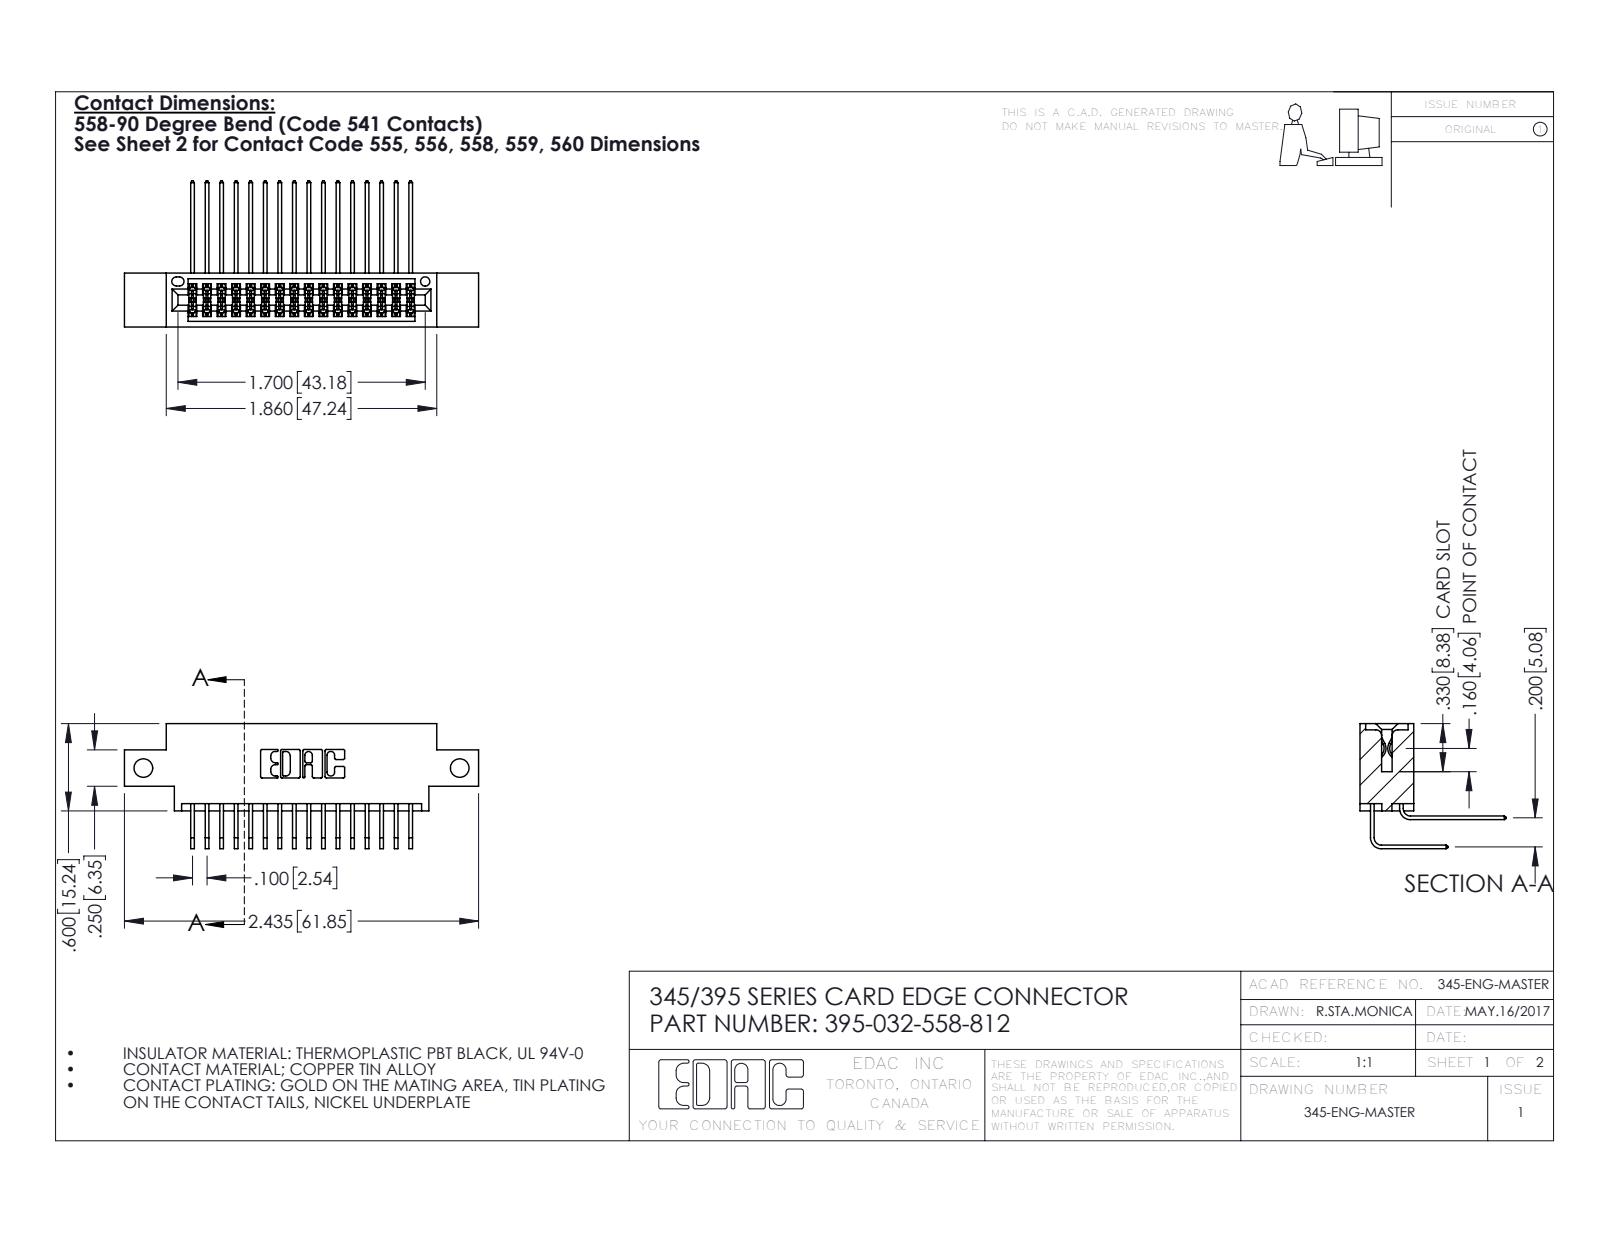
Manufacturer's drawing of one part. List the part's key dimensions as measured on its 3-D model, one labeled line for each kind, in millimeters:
Part name (STEP PRODUCT): 345-292-001_558 Tail - 2; 345 Part_0.170 Offset - Side Mount; 395-032-558-812; 345-292-001_558 559 Tail - 1
STEP written by: SolidWorks 2016 (CONFIG_CONTROL_DESIGN)
Units: millimetres
Bodies: 33 solids, 1794 faces (1204 planar, 590 cylindrical, 0 other)
Overall size (bounding box): 61.8 × 25.5 × 21.8
Volume: 5 750 mm³ · Surface area: 8 871 mm²
Round holes (diameter × count): ⌀3.3 ×2, ⌀1.6 ×1
Partial cylindrical surfaces — rounded edges, fillets, slot ends (radius × count): R0.2 ×49, R0.3 ×22, R0.2 ×6, R0.8 ×6, R0.7 ×3, R0.4 ×2, R0.5 ×2, R0.6 ×2
Main face-to-face distances: 5.1, 1.8, 7.6, 9.4, 2.5, 6.9, 0.6, 5.7, 2.5, 4.4
Hole centre spacings: 55.2
